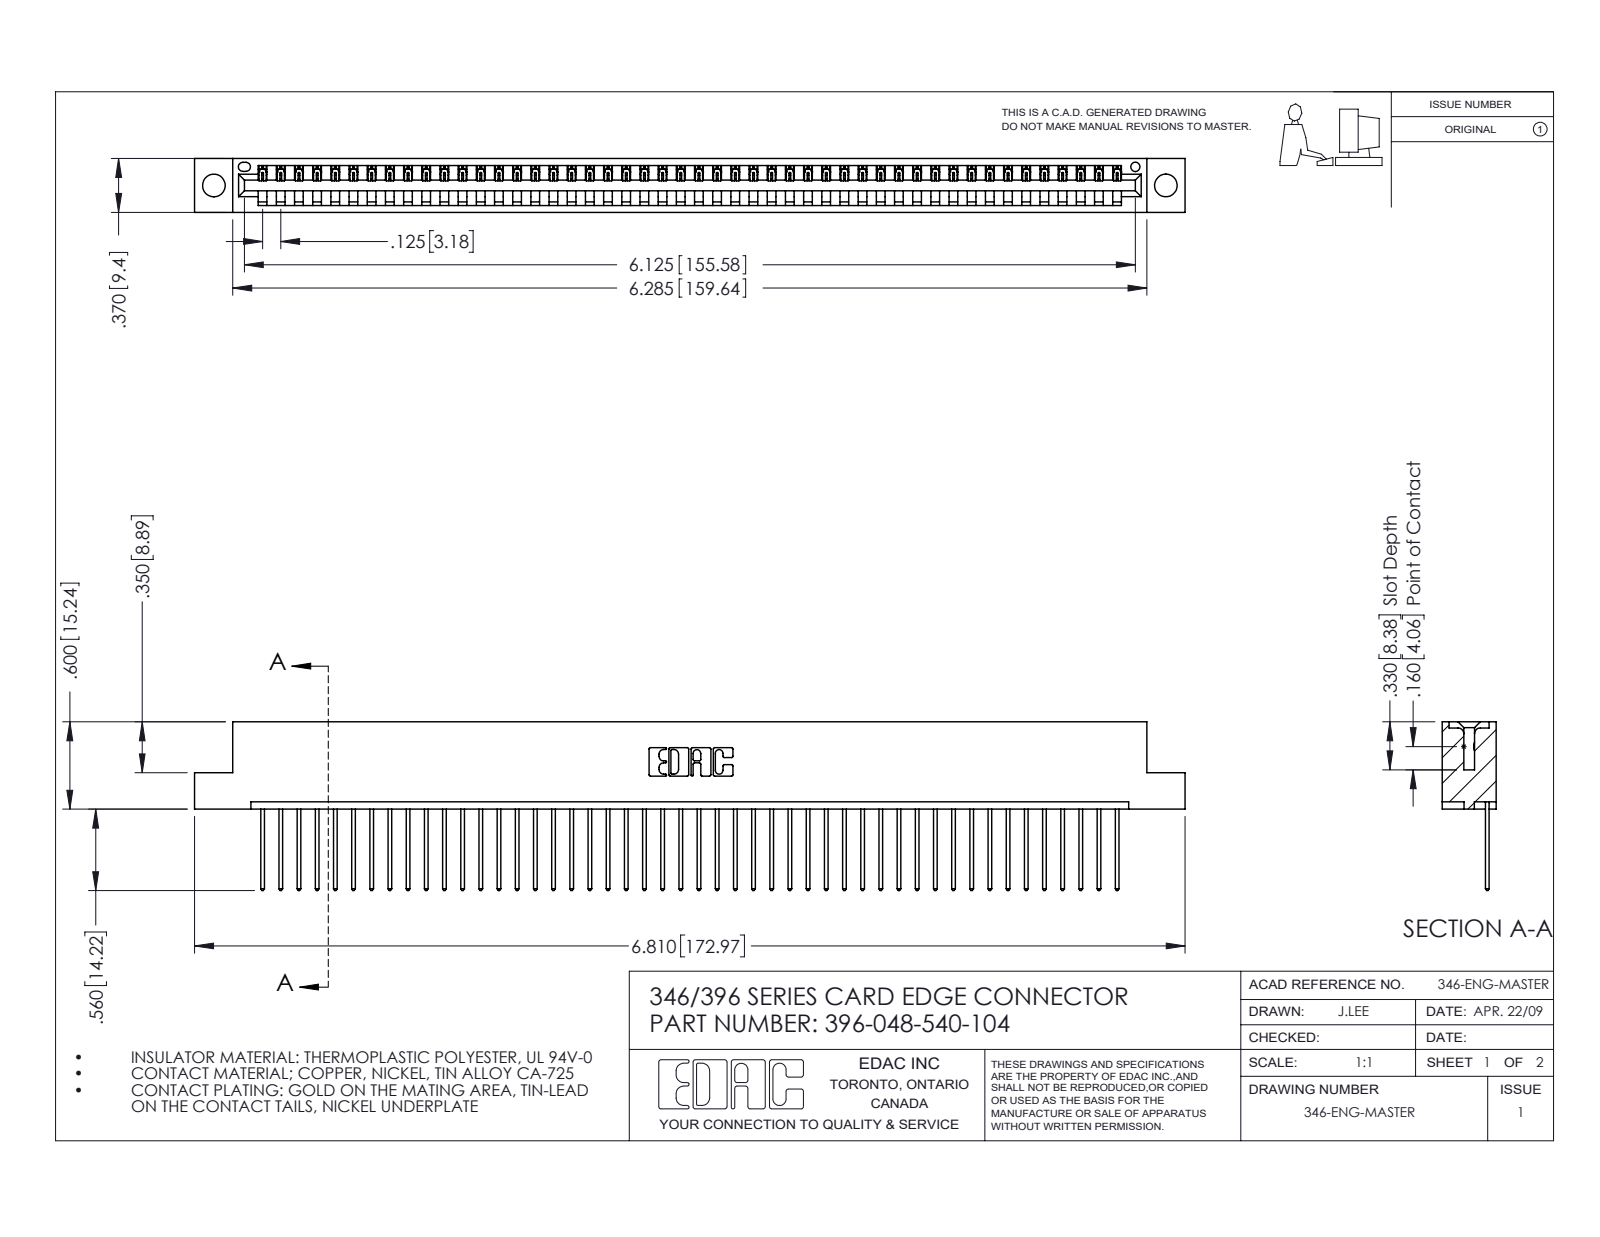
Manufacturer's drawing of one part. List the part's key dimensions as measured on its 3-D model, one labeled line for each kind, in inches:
Part name (STEP PRODUCT): 396-048-540-104; 346 Part_Flush Mounting Lugs - 0.156 Dia-TH; 345-292-001_345-293-140
STEP written by: SolidWorks 2016 (CONFIG_CONTROL_DESIGN)
Units: inches
Bodies: 49 solids, 2906 faces (1996 planar, 910 cylindrical, 0 other)
Overall size (bounding box): 6.81 × 1.16 × 0.37
Volume: 1.012 in³ · Surface area: 32.65 in²
Round holes (diameter × count): ⌀0.156 ×2, ⌀0.064 ×1
Partial cylindrical surfaces — rounded edges, fillets, slot ends (radius × count): R0.006 ×96, R0.01 ×96, R0.01 ×22, R0.007 ×6, R0.031 ×6, R0.026 ×3, R0.031 ×2, R0.04 ×2
Main face-to-face distances: 0.048, 0.322, 0.37, 0.25, 0.072, 0.298, 0.025, 0.148, 0.222, 0.1
Hole centre spacings: 0.246, 6.336, 6.545
